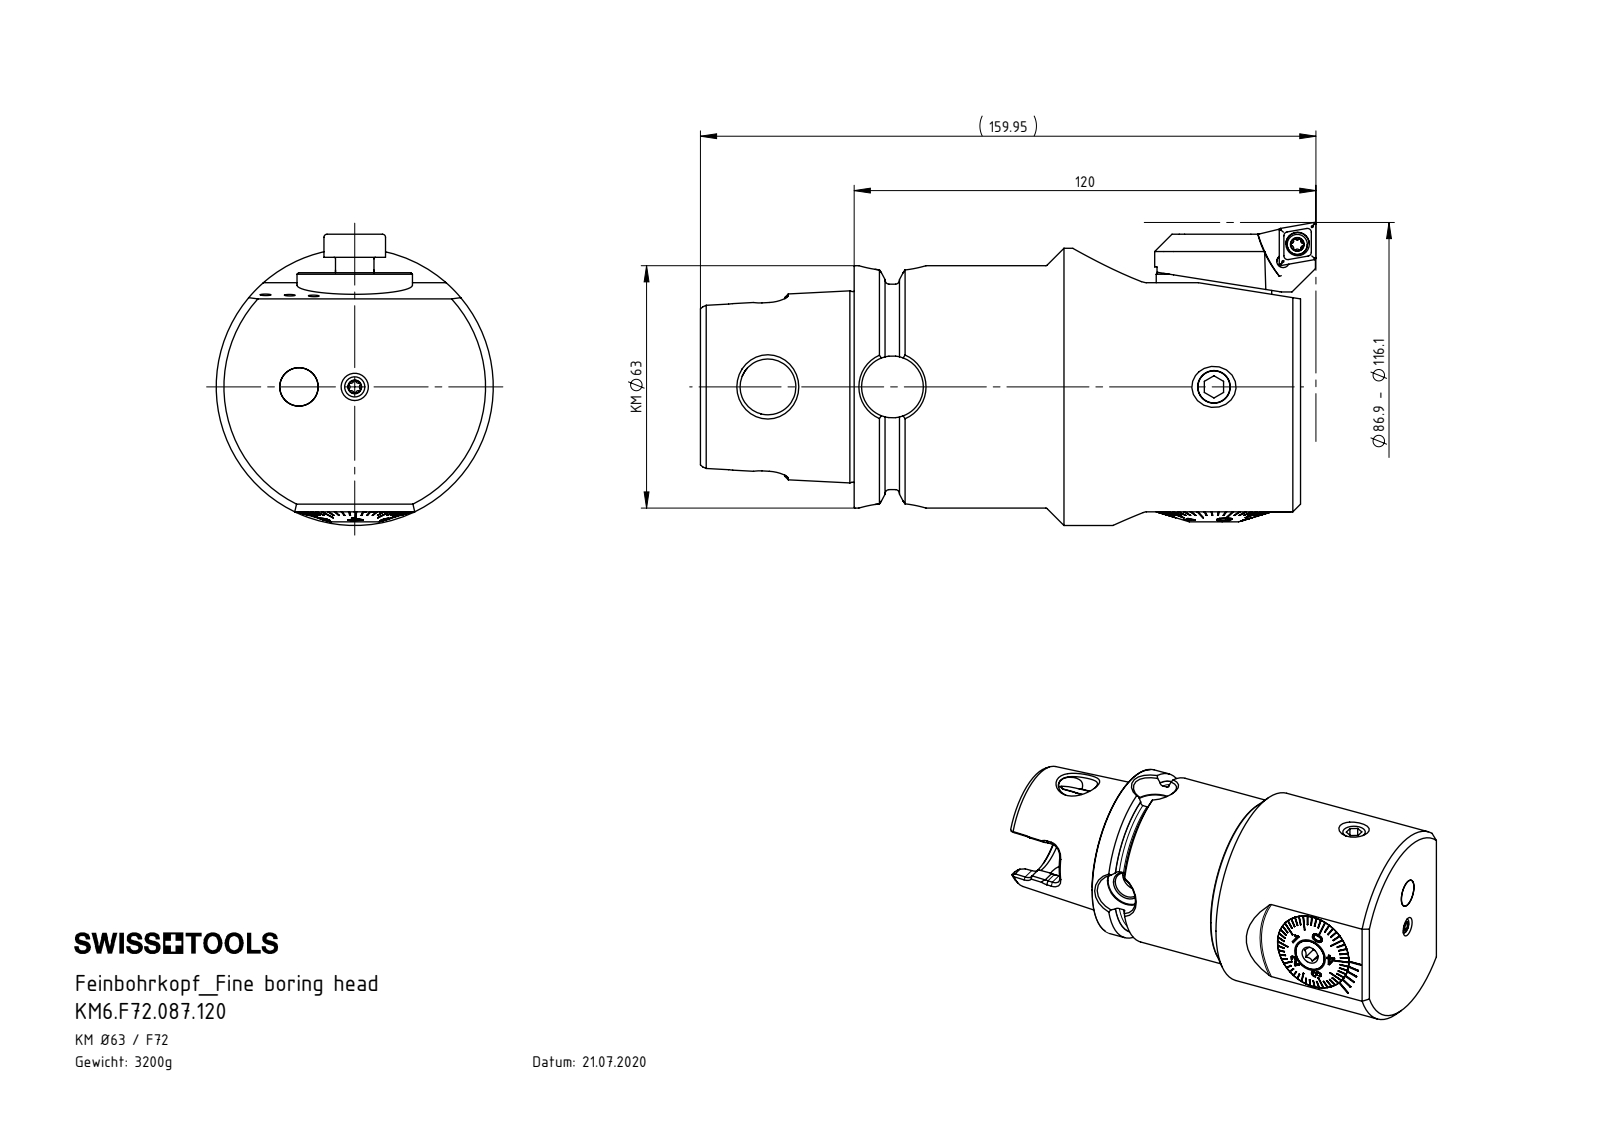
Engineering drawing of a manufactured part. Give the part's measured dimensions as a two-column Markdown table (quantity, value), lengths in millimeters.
| quantity | value |
| --- | --- |
| part name | F72-BG1.AA4.030; F55-BG1.012.012_A; DIN 3771 - 25x1.5; F72-BG1.DA3.030_A (+8 more) |
| STEP written by | SolidWorks 2017 (AUTOMOTIVE_DESIGN) |
| units | millimeters |
| bodies | 13 solids, 715 faces (344 planar, 108 cylindrical, 263 other) |
| overall size | 155.95 × 75.66 × 72 |
| volume | 410 406 mm³ |
| surface area | 70 852 mm² |
| round holes (diameter × count) | 2.5 × 3, 4.2 × 3, 3.3 × 2, 8.5 × 2, 16.06 × 2, 5 × 1, 8 × 1, 10 × 1, 10.1 × 1, 10.2 × 1, 11.4 × 1, 12 × 1 |
| round bosses / shafts (diameter × count) | 10 × 2, 72 × 1, 62.95 × 1, 30 × 1, 29.98 × 1, 29.9 × 1, 25 × 1, 18 × 1 |
| partial cylindrical surfaces (radius × count) | 0.34 × 6, 0.59 × 6, 2.5 × 6, 4 × 6, 2 × 4, 3.2 × 3, 0.5 × 2, 7.04 × 2 |
| main face-to-face distances | 116, 53.01, 1.1, 117.1, 2.6, 62.11, 59.51, 6.5, 2.5, 58.31 |
| hole center spacings | 83.55, 14.5, 17.97, 19.81, 29, 32.35, 98.13, 115.9 |
